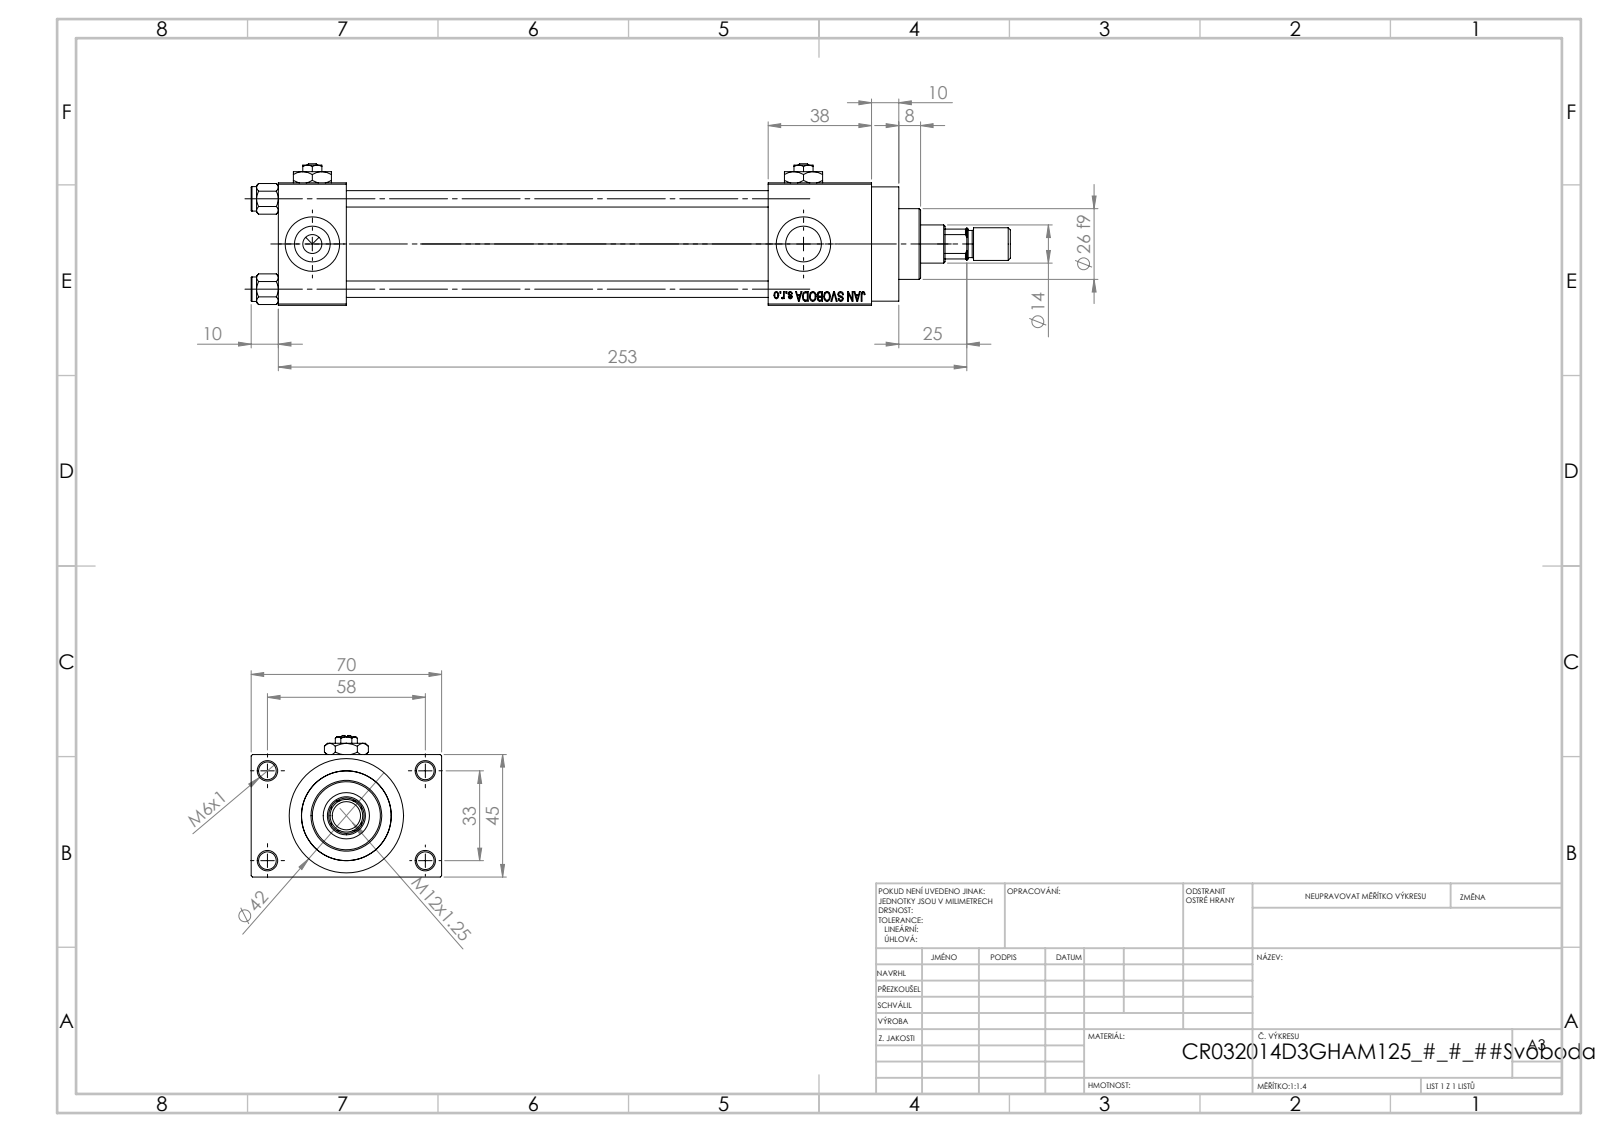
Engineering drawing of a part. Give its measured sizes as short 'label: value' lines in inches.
name: V215CR_D_Body; V215_VC_A; V215CR_VCP_D; V215CR_D_TYCINKA (+3 more)
written by: SolidWorks 2019 (CONFIG_CONTROL_DESIGN)
unit: in
bodies: 14 solids, 1215 faces (546 planar, 103 cylindrical, 566 other)
size: 10.984 × 2.756 × 2.047
volume: 17.91 in³; area: 176.1 in²
holes: 5× ⌀0.256, 4× ⌀0.236, 4× ⌀0.518, 4× ⌀0.787, 3× ⌀0.276, 1× ⌀0.551, 1× ⌀0.669, 1× ⌀0.945, 1× ⌀1.26, 1× ⌀1.299
bosses: 4× ⌀0.354, 1× ⌀1.654, 1× ⌀1.496, 1× ⌀1.024, 1× ⌀0.472, 1× ⌀0.394
rounds: 1× R0.256
face distances: 1.772, 0.984, 0.492, 6.102, 7.087, 2.264, 7.598, 1.496, 8.583, 2.756
hole spacings: 0.488, 0.924, 1.307, 1.314, 1.392, 1.795, 2.219, 1.299
